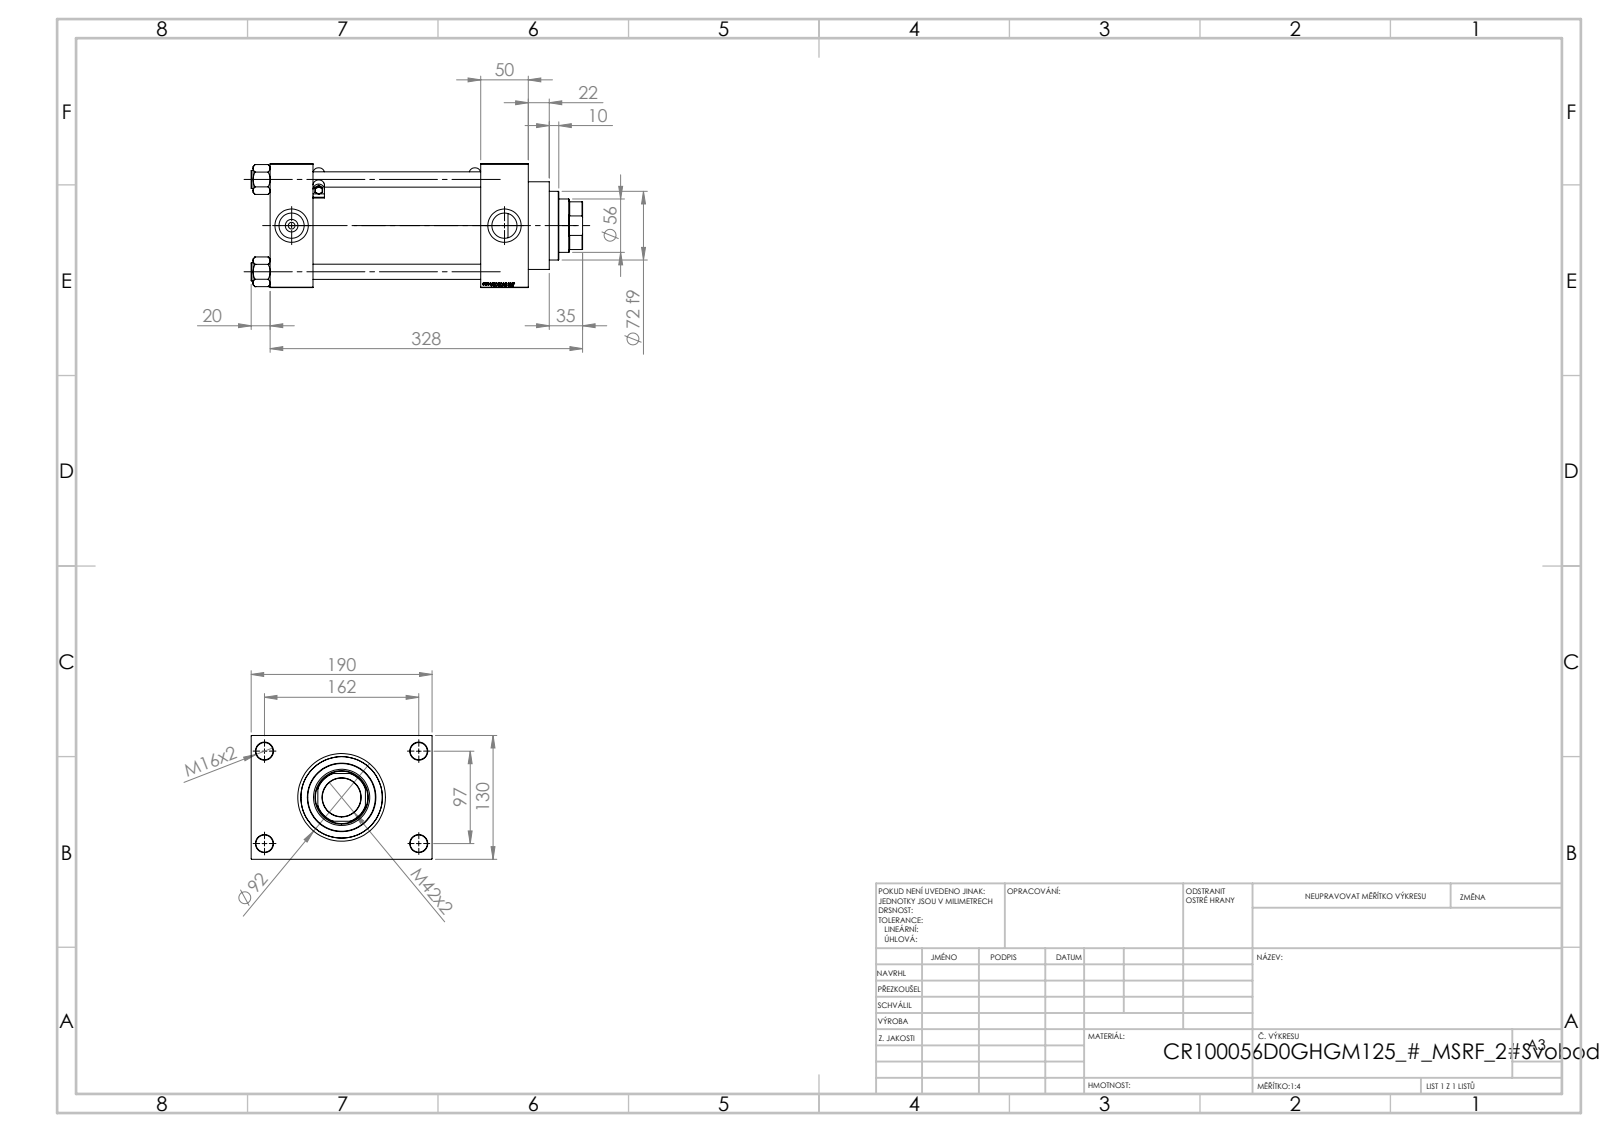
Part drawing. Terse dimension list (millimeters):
name: V215CR_VCP_D; V215CR_D_Body; MSRF_MSRG1; NUT_M5_D (+2 more)
written by: SolidWorks 2019 (CONFIG_CONTROL_DESIGN)
unit: mm
bodies: 13 solids, 1215 faces (581 planar, 116 cylindrical, 518 other)
size: 348 × 190 × 130
volume: 3 081 000 mm³; area: 474 609 mm²
holes: 4× ⌀16, 4× ⌀18, 2× ⌀7, 2× ⌀26.44, 2× ⌀35, 1× ⌀40.5, 1× ⌀56, 1× ⌀59, 1× ⌀76, 1× ⌀85.5, 1× ⌀100
bosses: 4× ⌀19, 2× ⌀5, 2× ⌀2.5, 1× ⌀106, 1× ⌀92, 1× ⌀72
rounds: 12× R0.5, 4× R6, 1× R27
face distances: 130, 50, 45, 221, 176, 271, 226, 30, 160, 190
hole spacings: 32.55, 68.52, 94.41, 96.9, 102.27, 129.45, 161.73, 97
